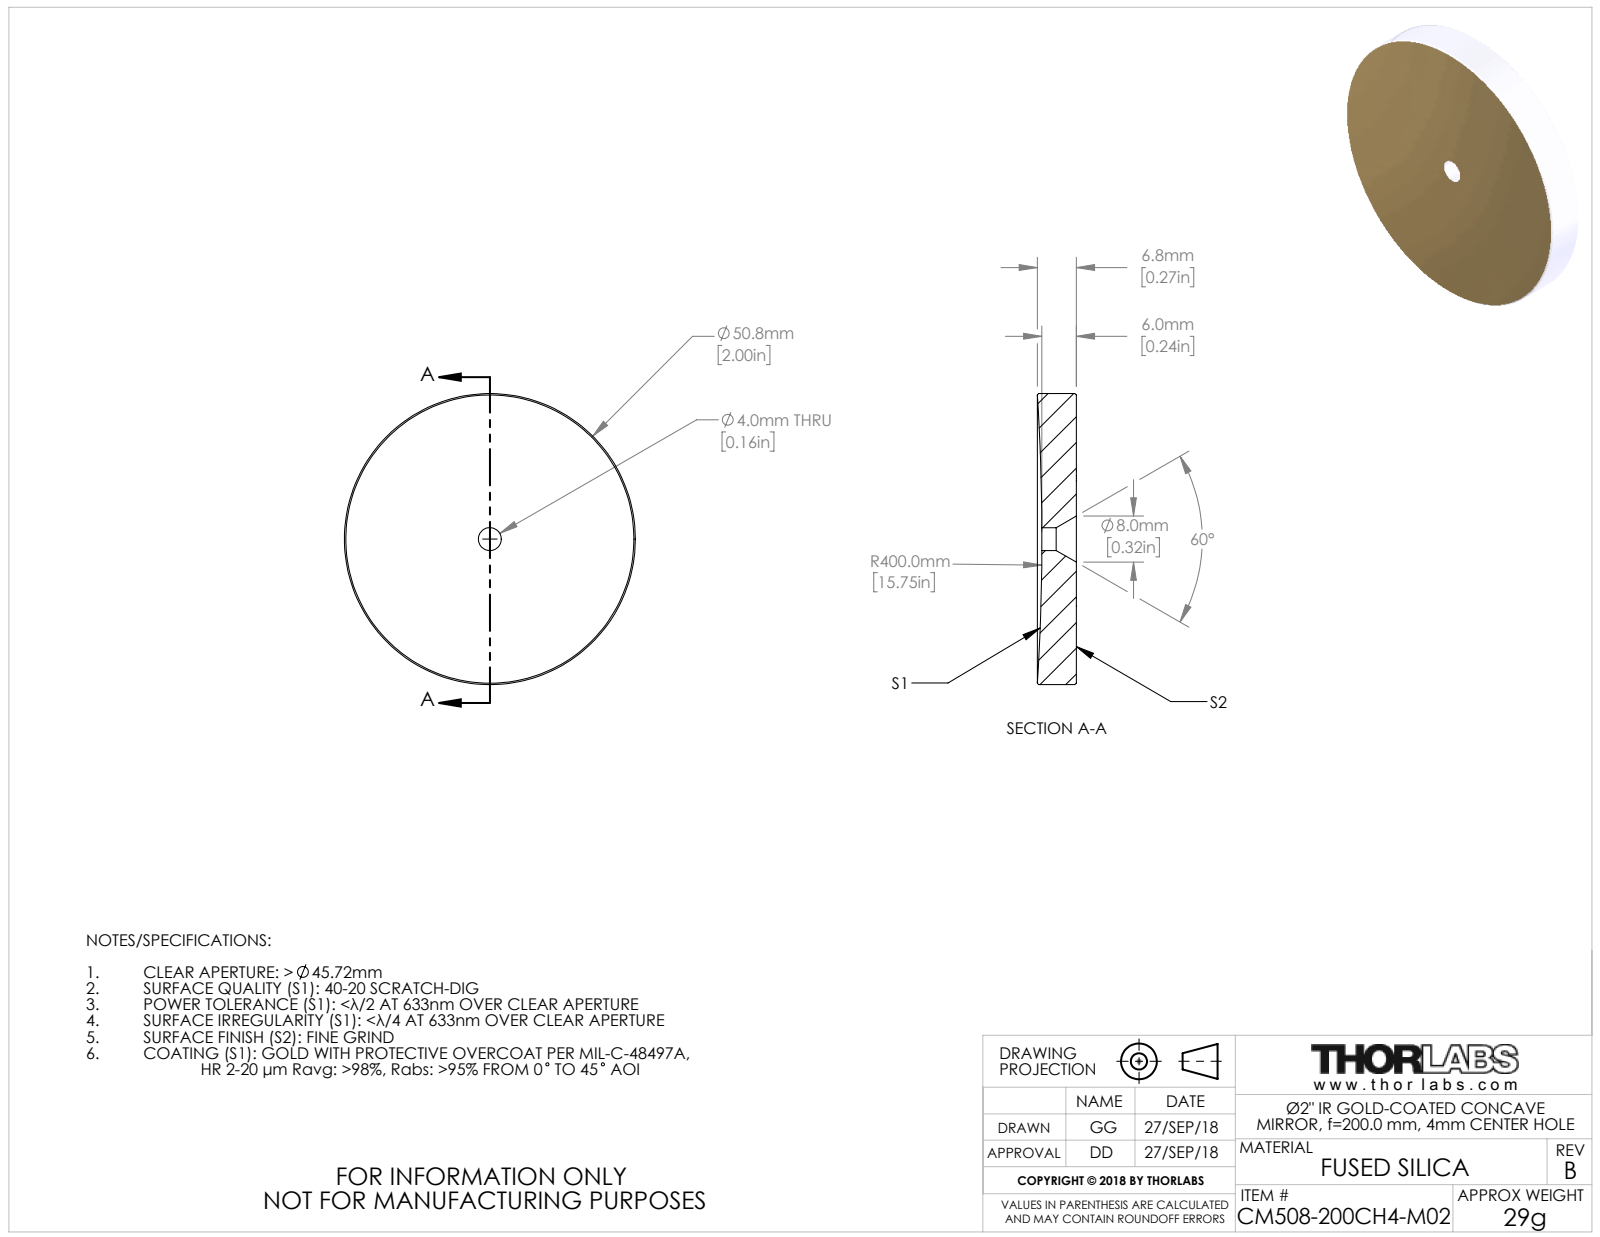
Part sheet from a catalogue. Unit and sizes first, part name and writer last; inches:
Units: inches
Overall size (bounding box): 2 × 2 × 0.267
Round holes (diameter × count): ⌀0.157 ×1
Round bosses / shafts (diameter × count): ⌀2 ×1
Volume: 0.783 in³ · Surface area: 7.965 in²
Bodies: 1 solid, 49 faces (37 planar, 4 cylindrical, 8 other)
Part name (STEP PRODUCT): TTN028026-E0W
STEP written by: SolidWorks 2014 (CONFIG_CONTROL_DESIGN)
